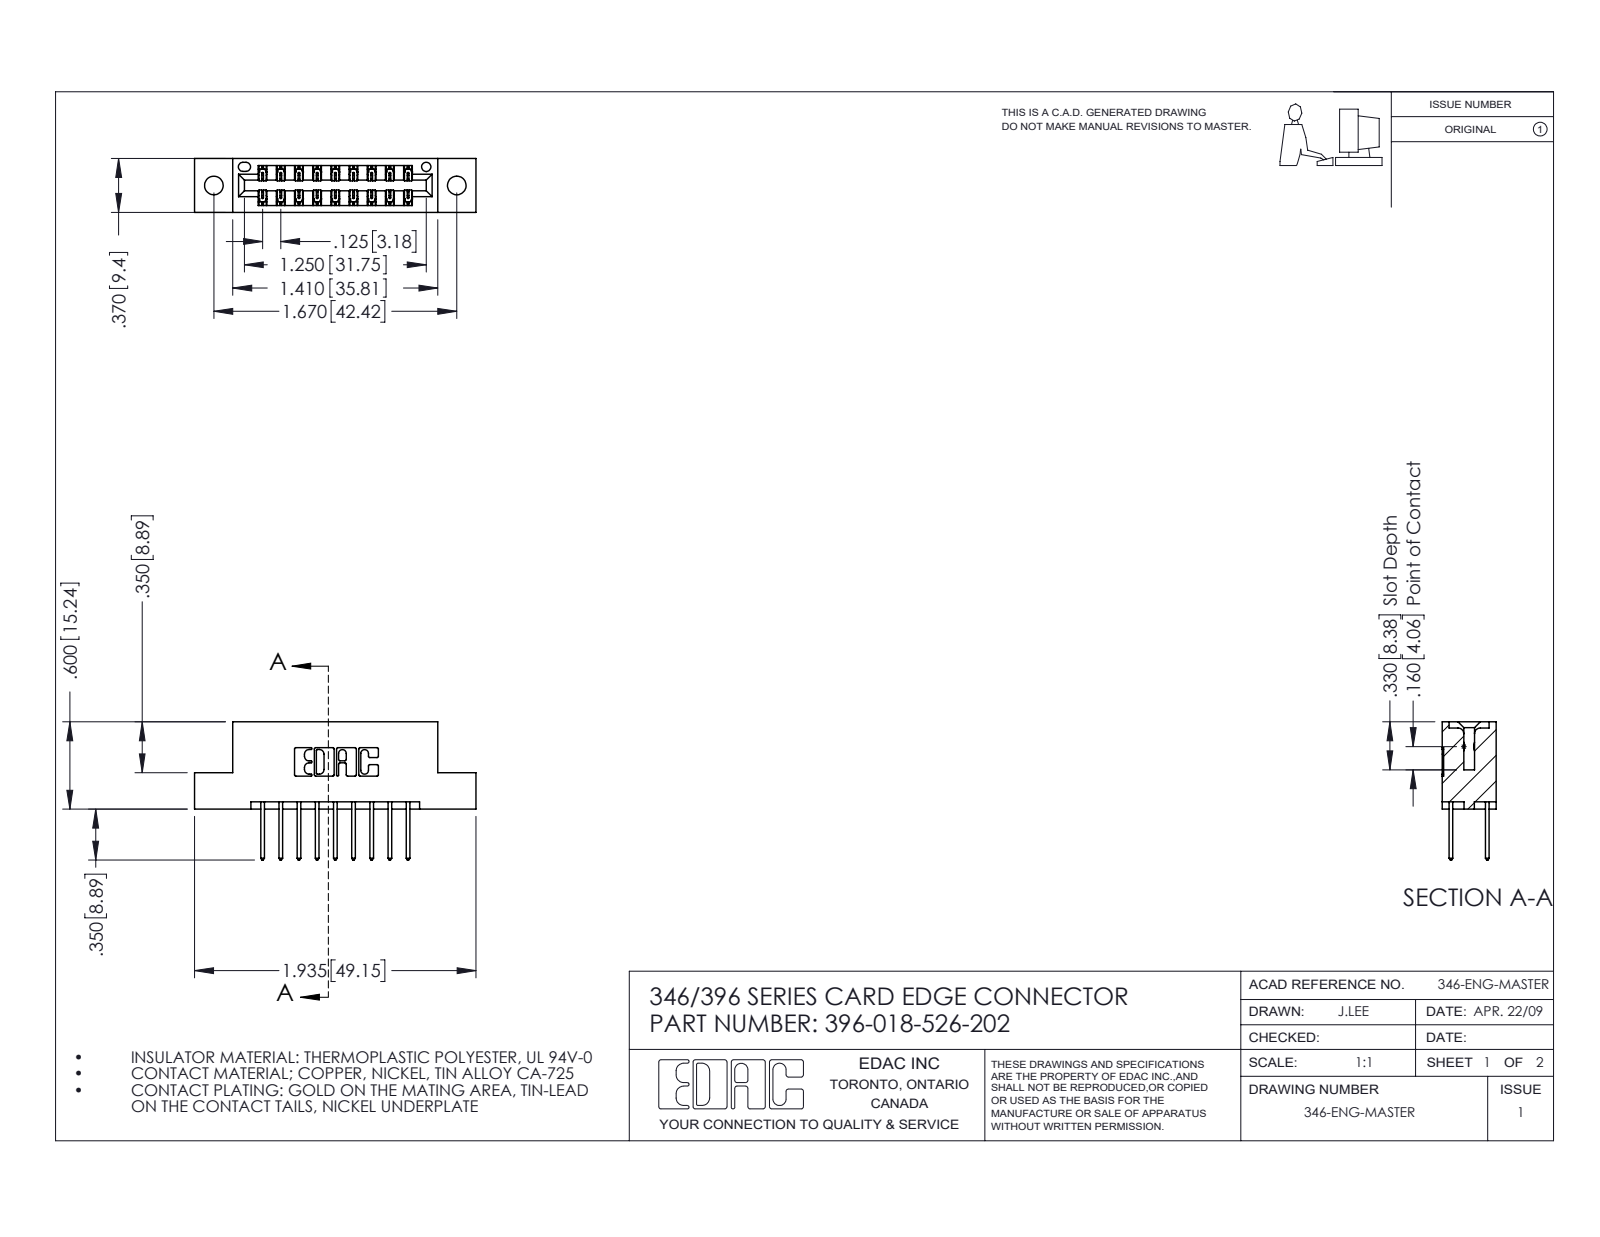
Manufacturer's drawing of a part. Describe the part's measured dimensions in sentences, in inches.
The part is named "396-018-526-202; 346 Part_Flush Mounting Lugs - 0.128 Dia; 345-292-001_345-293-126". Its 3-D file was written by "SolidWorks 2016 (CONFIG_CONTROL_DESIGN)". It is 19 solids with 1058 faces: 706 planar, 352 cylindrical and 0 other. Overall it measures 1.935 by 0.95 by 0.37 inches. Its volume is 0.276 cubic inches and its surface area 8.633 square inches. Round holes: 2 of diameter 0.128, 1 of diameter 0.064. Partial cylindrical surfaces (rounded edges, fillets, slot ends): 27 of radius 0.006, 22 of radius 0.01, 18 of radius 0.01, 6 of radius 0.007, 6 of radius 0.031, 3 of radius 0.026, 2 of radius 0.014, 2 of radius 0.022. The main face-to-face distances are 0.25, 0.048, 0.322, 0.37, 0.072, 0.298, 0.025, 0.275, 0.148, 0.222. The hole center spacings are 0.246, 1.465, 1.67.
